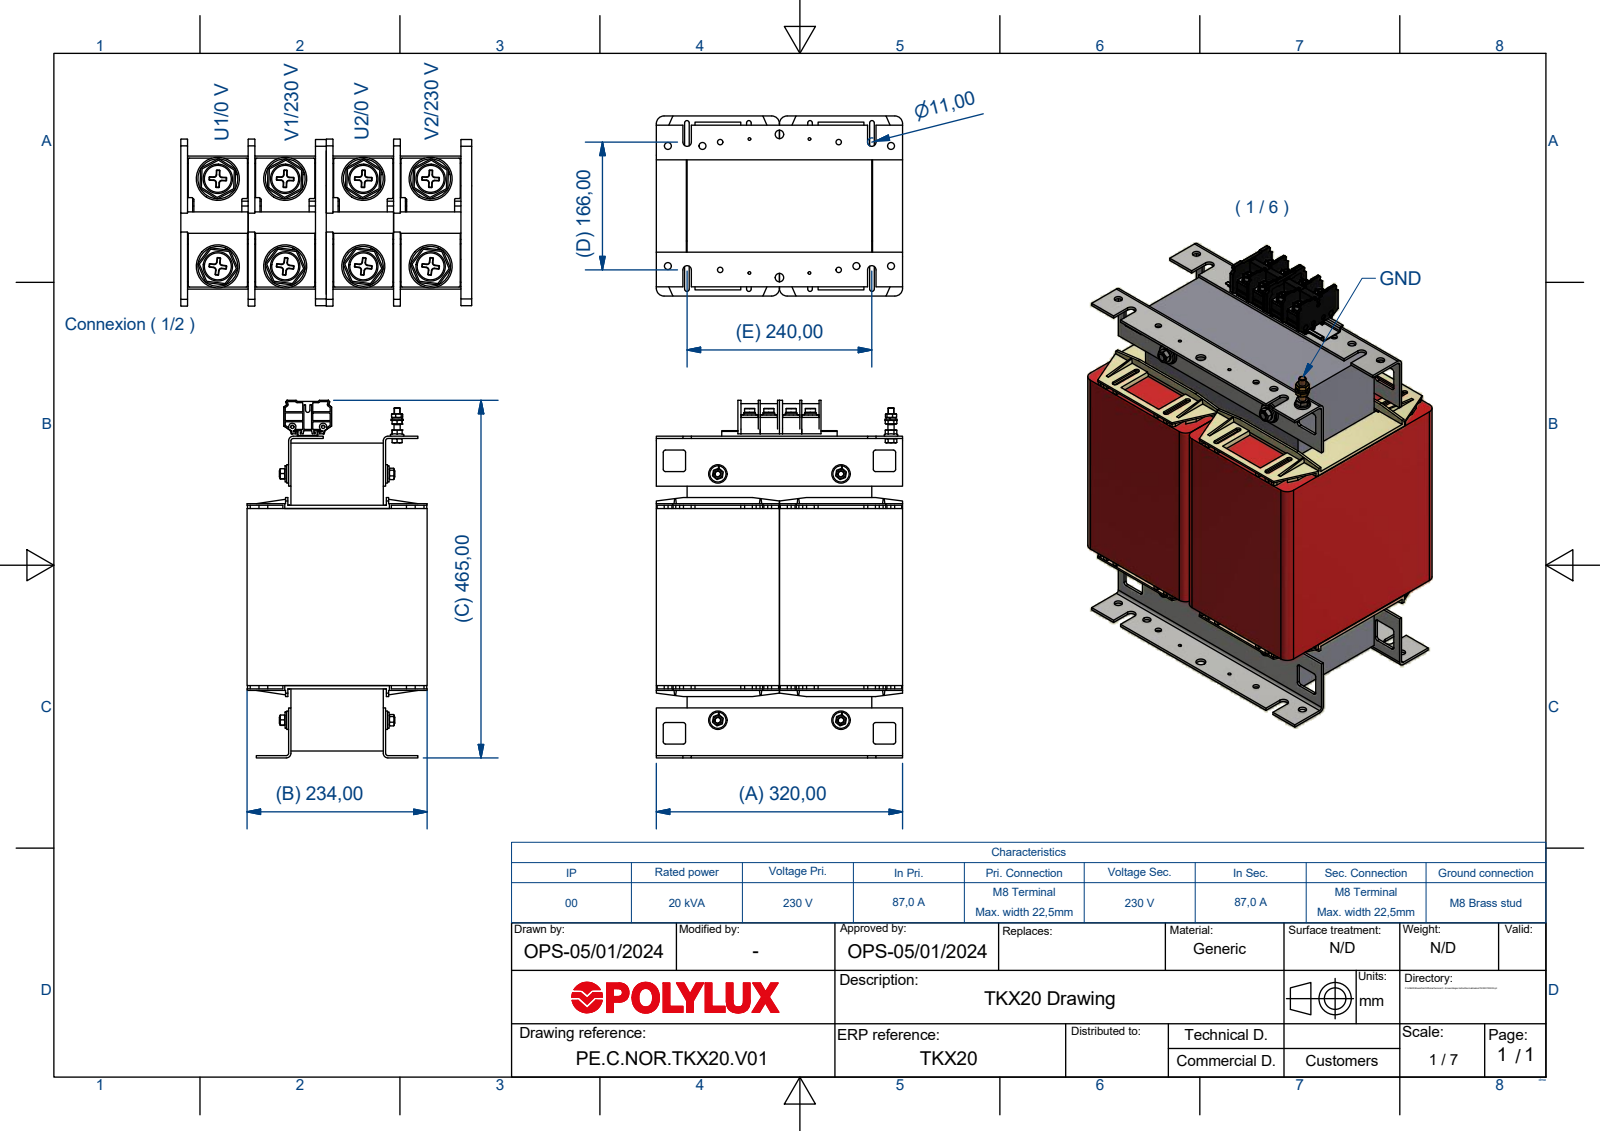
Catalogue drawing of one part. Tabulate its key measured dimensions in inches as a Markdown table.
| quantity | value |
| --- | --- |
| part name | TKX20 |
| STEP written by | Autodesk Inventor 2018 (AUTOMOTIVE_DESIGN) |
| units | inches |
| bodies | 87 solids, 5582 faces (2094 planar, 2030 cylindrical, 1458 other) |
| overall size | 18.292 × 12.598 × 9.213 |
| volume | 1 377 in³ |
| surface area | 3 260 in² |
| round holes (diameter × count) | 0.354 × 10, 0.331 × 9, 0.335 × 9, 0.315 × 8, 0.394 × 8, 0.138 × 6, 0.276 × 6, 0.262 × 5, 0.472 × 4, 0.5 × 4, 0.512 × 4, 0.165 × 3 |
| round bosses / shafts (diameter × count) | 0.63 × 9, 0.583 × 8, 0.398 × 8, 0.309 × 8, 0.315 × 5, 0.945 × 4, 0.831 × 4, 0.5 × 1 |
| partial cylindrical surfaces (radius × count) | 0.006 × 839, 0.02 × 64, 0.004 × 56, 0.039 × 36, 0.118 × 36, 0.014 × 32, 0.01 × 8, 0.394 × 8 |
| main face-to-face distances | 6.299, 4.724, 4.941, 1.358, 4.961, 0.236, 0.039, 0.118, 3.583, 0.217 |
| hole center spacings | 4.843, 4.57, 1.504, 1.554, 2.684, 3.057, 4.188, 5.739 |
